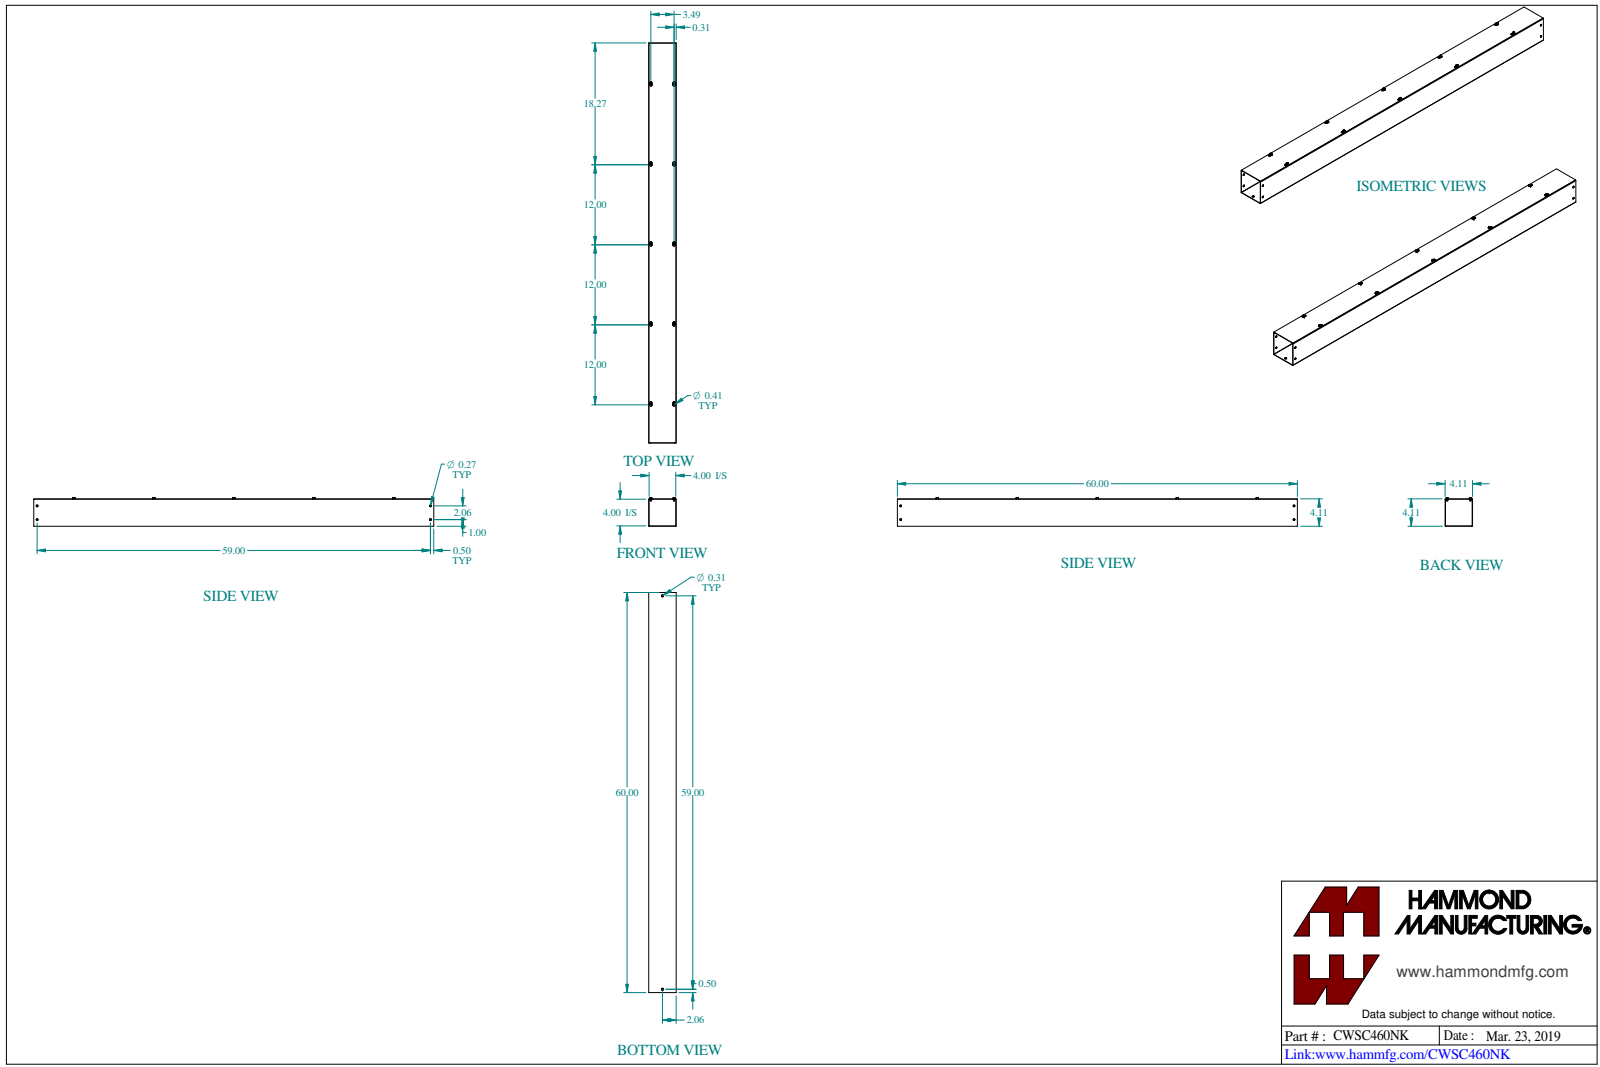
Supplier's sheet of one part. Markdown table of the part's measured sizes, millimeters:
| quantity | value |
| --- | --- |
| part name | CWSC460NK |
| STEP written by | SolidWorks 2023 (CONFIG_CONTROL_DESIGN) |
| units | millimeters |
| bodies | 12 solids, 366 faces (178 planar, 128 cylindrical, 60 other) |
| overall size | 1524 × 108.9 × 104.5 |
| volume | 950 400 mm³ |
| surface area | 1 323 000 mm² |
| round holes (diameter × count) | 4.5 × 10, 6.8 × 4, 8 × 2 |
| round bosses / shafts (diameter × count) | 9.5 × 10, 4.8 × 10 |
| partial cylindrical surfaces (radius × count) | 3.2 × 10, 5.2 × 10, 0.7 × 4, 2.2 × 4 |
| main face-to-face distances | 1.4, 103, 101.6, 104.5, 100.2, 2.9, 0.8, 103.7, 0.7, 102.3 |
| hole center spacings | 304.8, 317.4, 609.6, 616, 88.6, 146.6, 446.7, 750.6 |
